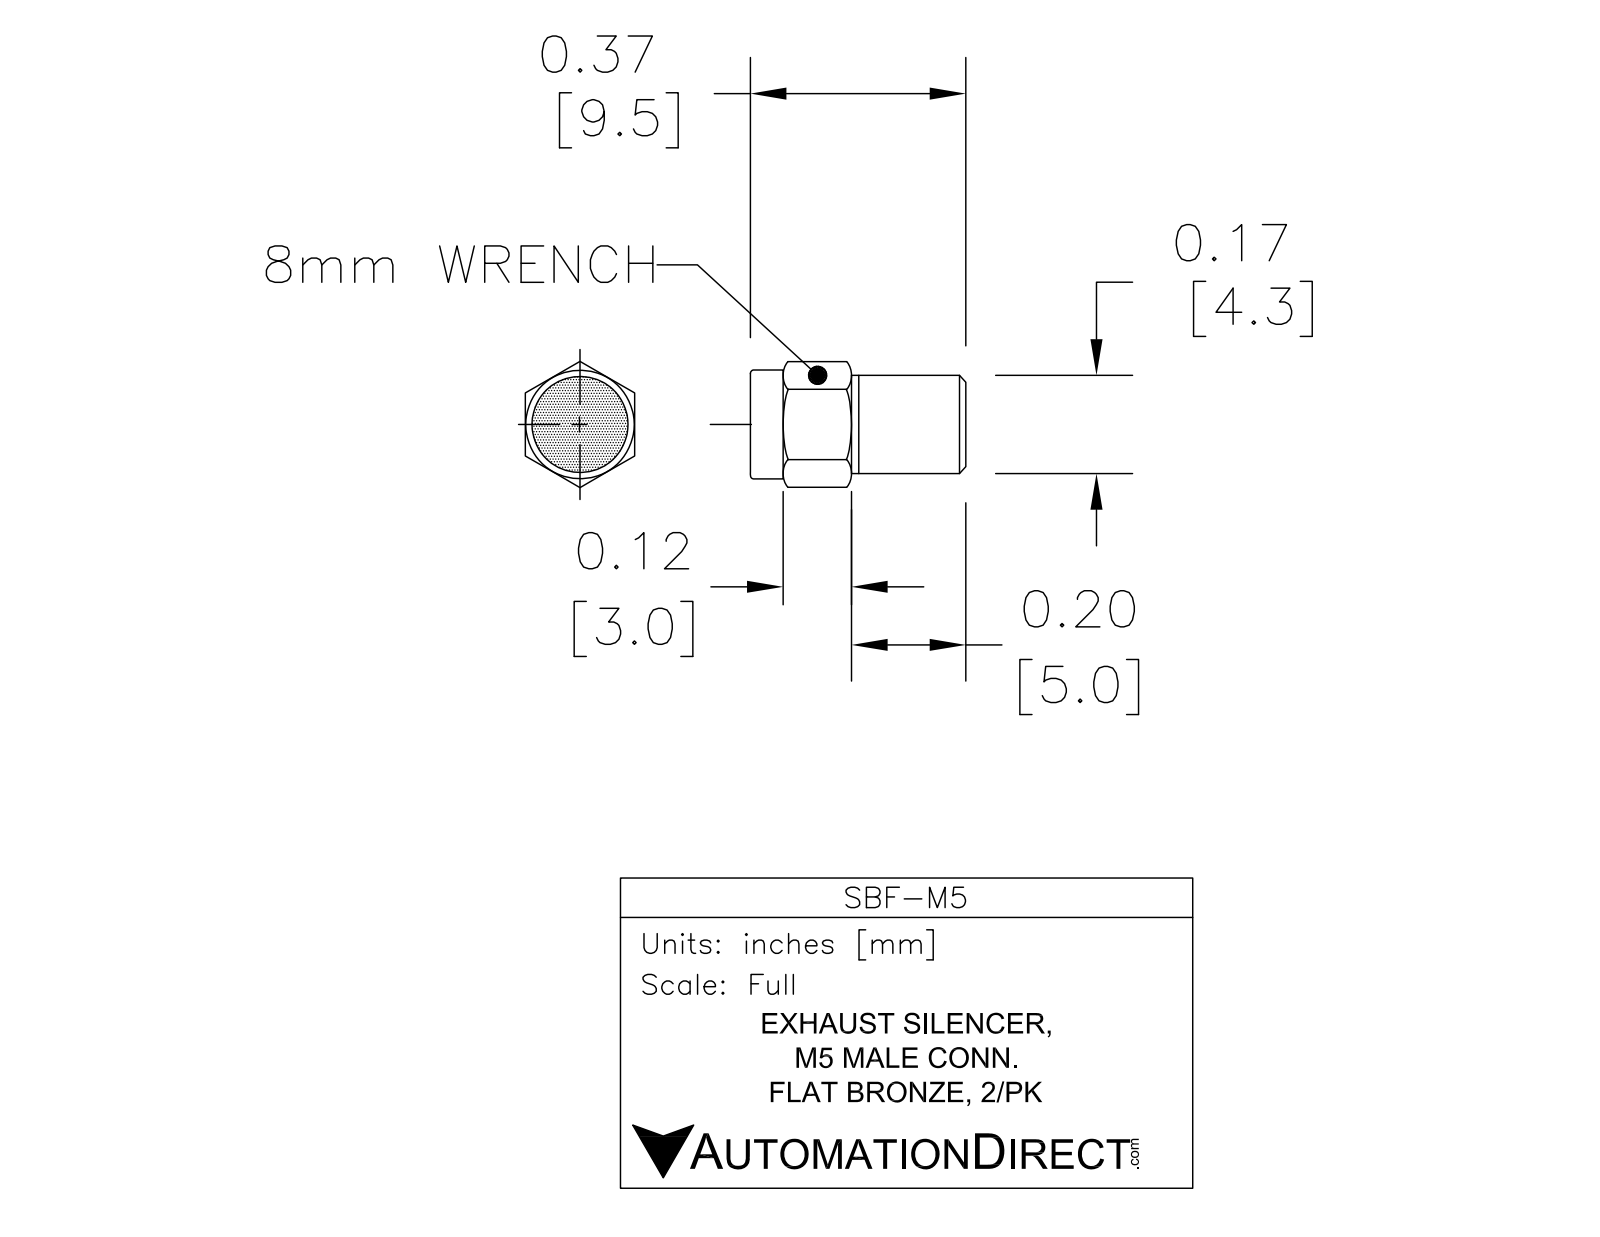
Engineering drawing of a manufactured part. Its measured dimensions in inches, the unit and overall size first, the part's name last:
Units: inches
Overall size (bounding box): 0.35 × 0.31 × 0.268
Round holes (diameter × count): ⌀0.125 ×1
Round bosses / shafts (diameter × count): ⌀0.23 ×1, ⌀0.196 ×1
Main face-to-face distances: 0.269, 0.03, 0.15, 0.12, 0.2, 0.32, 0.35, 0.17, 0.18
Volume: 0.01 in³ · Surface area: 0.555 in²
Bodies: 1 solid, 48 faces (12 planar, 16 cylindrical, 20 other)
Part name (STEP PRODUCT): SBF-M5
STEP written by: SolidWorks 2015 (CONFIG_CONTROL_DESIGN)
